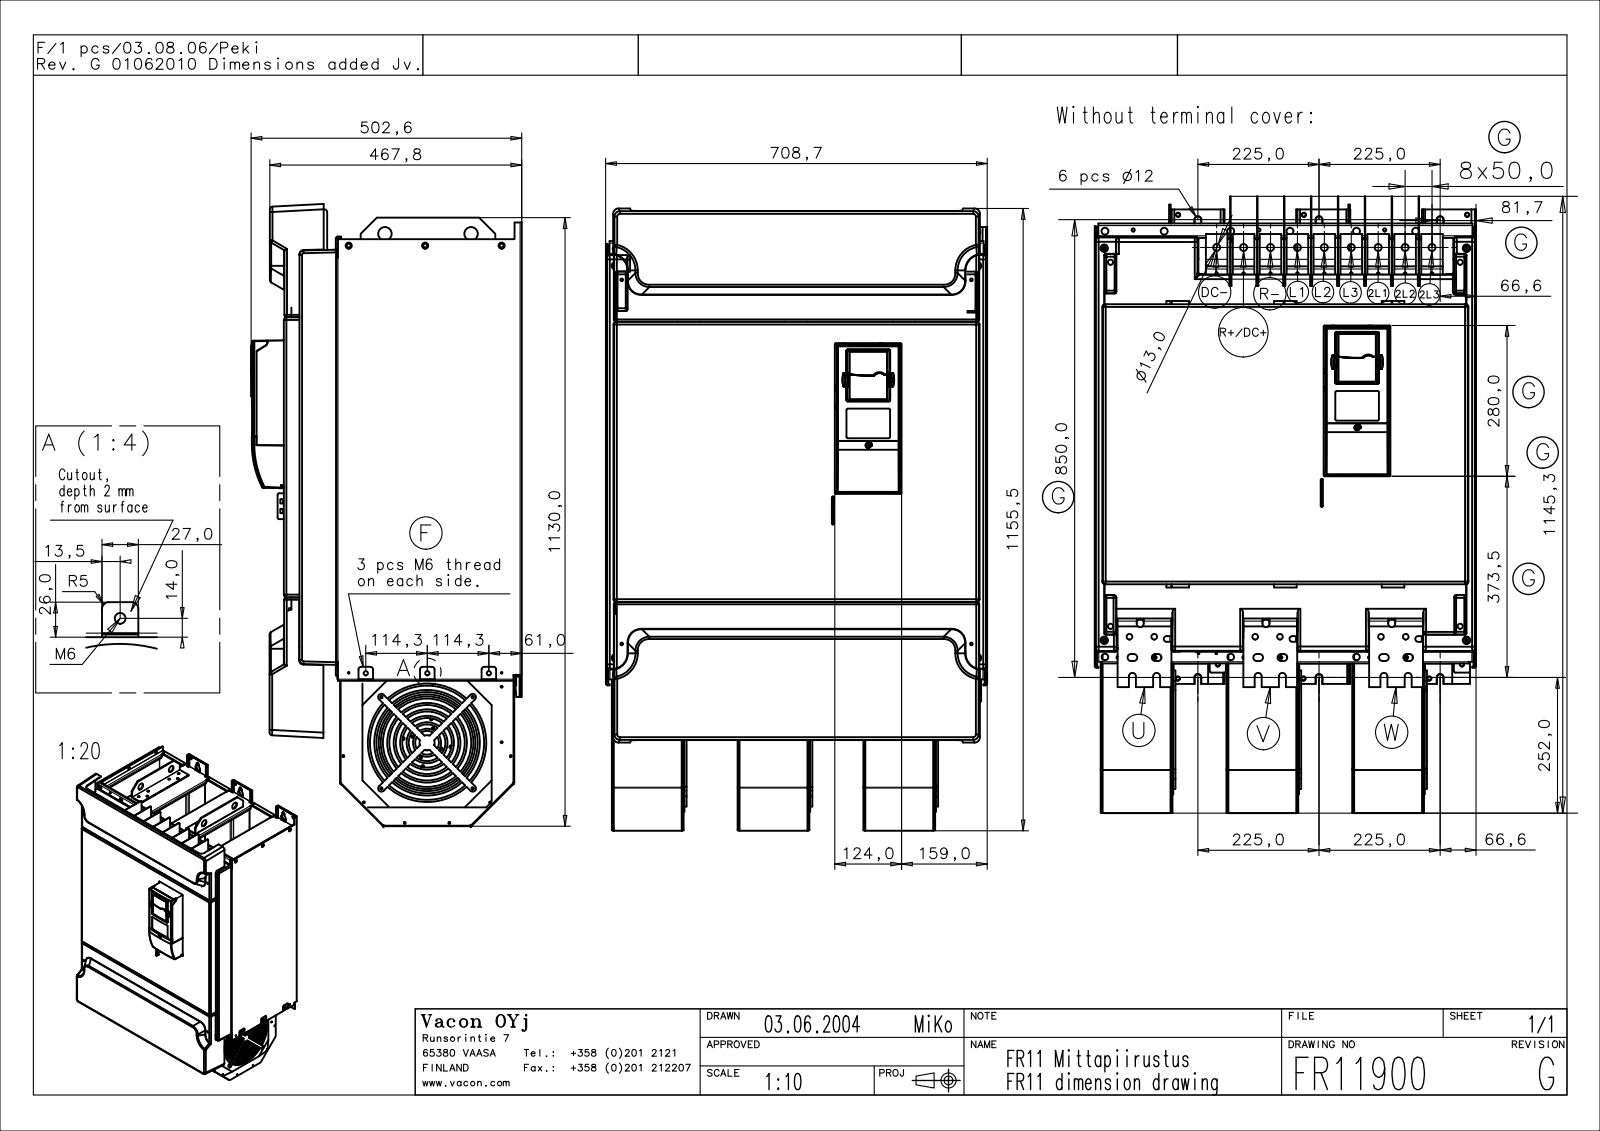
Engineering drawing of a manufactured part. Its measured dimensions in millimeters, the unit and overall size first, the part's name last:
Units: millimetres
Overall size (bounding box): 1206.16 × 712 × 522.59
Round holes (diameter × count): ⌀3.2 ×108, ⌀4.5 ×59, ⌀3.3 ×48, ⌀3.5 ×48, ⌀3.4 ×40, ⌀6.5 ×24, ⌀6 ×18, ⌀7 ×16, ⌀8 ×14, ⌀5 ×13, ⌀5.5 ×12, ⌀6.4 ×12
Round bosses / shafts (diameter × count): ⌀4 ×18, ⌀10 ×16, ⌀8.8 ×12, ⌀7.8 ×12, ⌀6.6 ×12, ⌀9.5 ×11, ⌀9.2 ×10, ⌀6 ×9
Partial cylindrical surfaces — rounded edges, fillets, slot ends (radius × count): R3 ×201, R1 ×165, R0.2 ×135, R5 ×135, R4 ×124, R0.5 ×123, R2 ×104, R0.15 ×57
Main face-to-face distances: 2, 233.58, 0.49, 3, 4, 235.58, 3.51, 135, 706.2, 413
Hole centre spacings: 3.25, 32.02, 283.11, 2.5, 4.8, 160, 233.58, 239.01
Bodies: 24 solids, 8911 faces (4014 planar, 3734 cylindrical, 1163 other)
Part name (STEP PRODUCT): OUT_NXP_FR11
STEP written by: CREO PARAMETRIC BY PTC INC, 2018070 (CONFIG_CONTROL_DESIGN)
